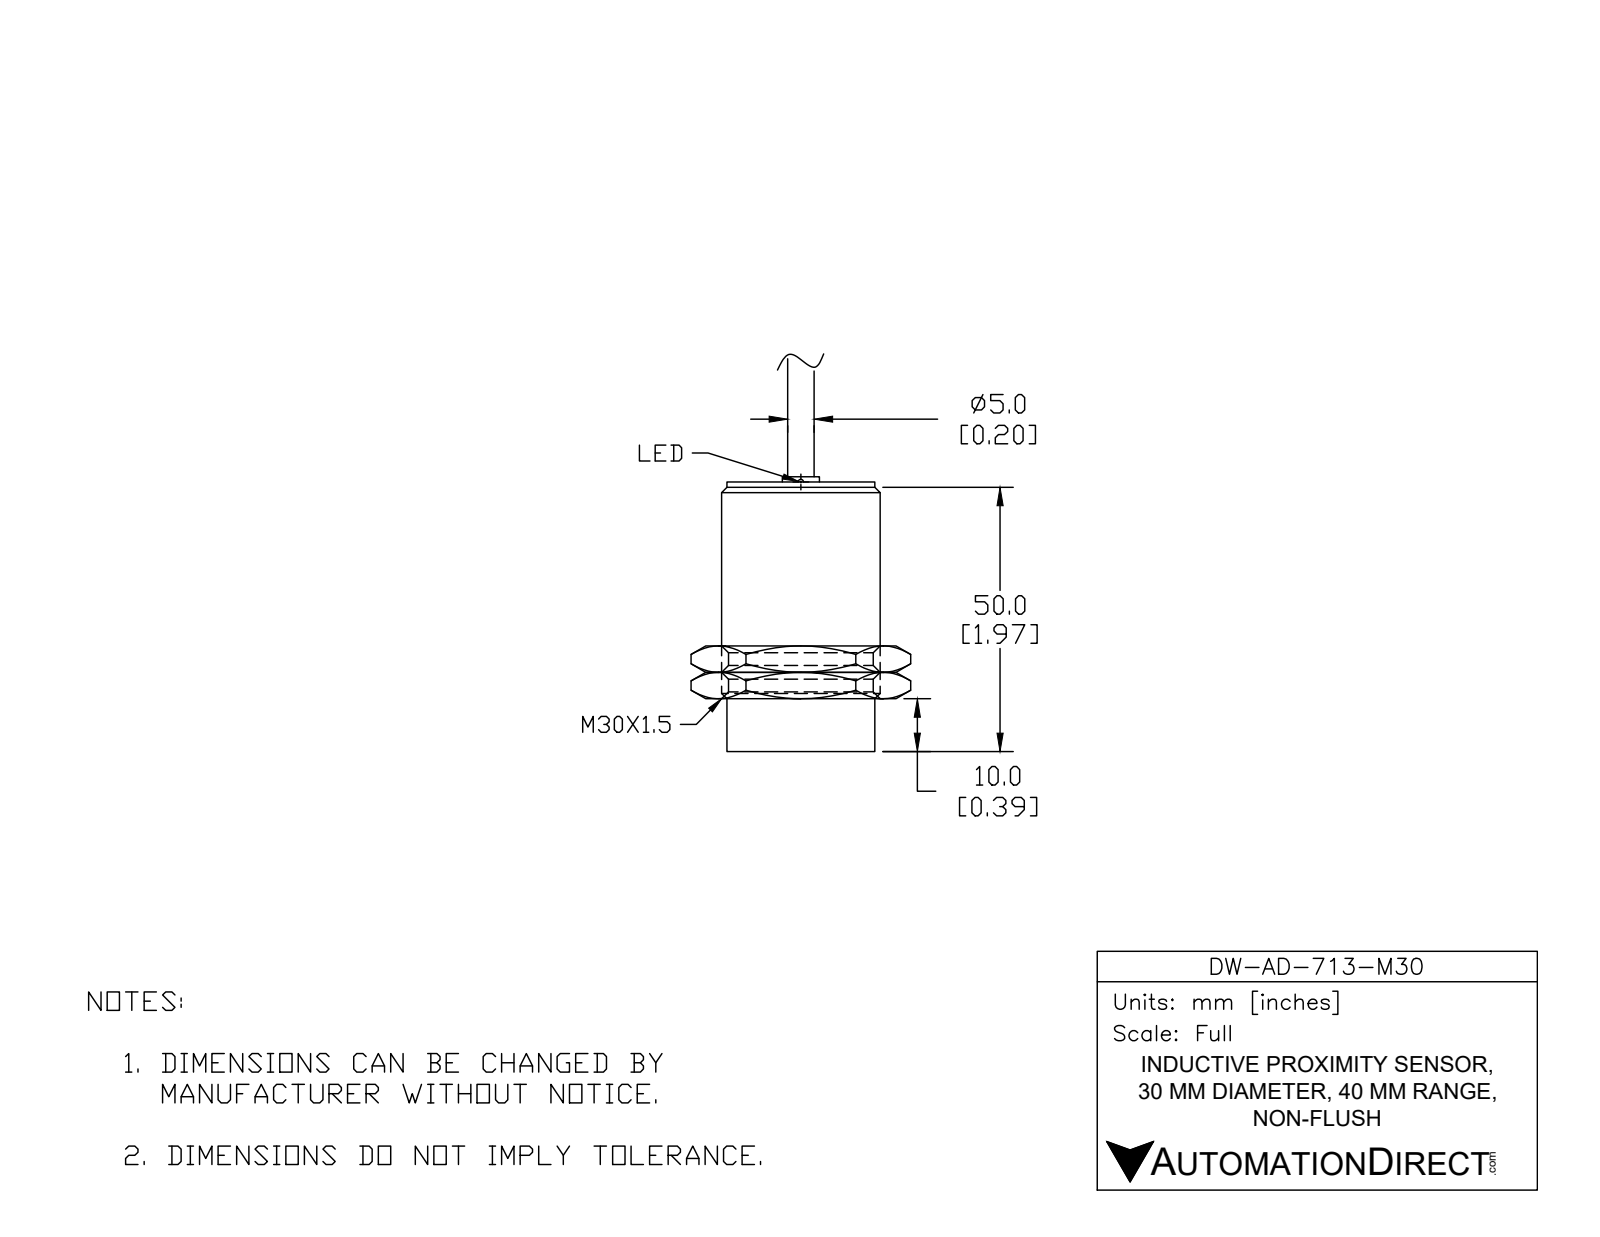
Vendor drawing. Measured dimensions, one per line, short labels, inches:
name: DW-AD-713-M30
written by: SolidWorks 2017 (AUTOMOTIVE_DESIGN)
unit: in
bodies: 2 solids, 37 faces (18 planar, 7 cylindrical, 12 other)
size: 3.016 × 1.181 × 1.181
volume: 2.159 in³; area: 10.1 in²
bosses: 1× ⌀1.181, 1× ⌀1.083, 1× ⌀0.413, 1× ⌀0.268, 1× ⌀0.197, 1× ⌀0.118
face distances: 2.008, 0.031, 2.087, 0.079, 2.039, 0.047, 1.89, 0.118, 0.15, 0.197
